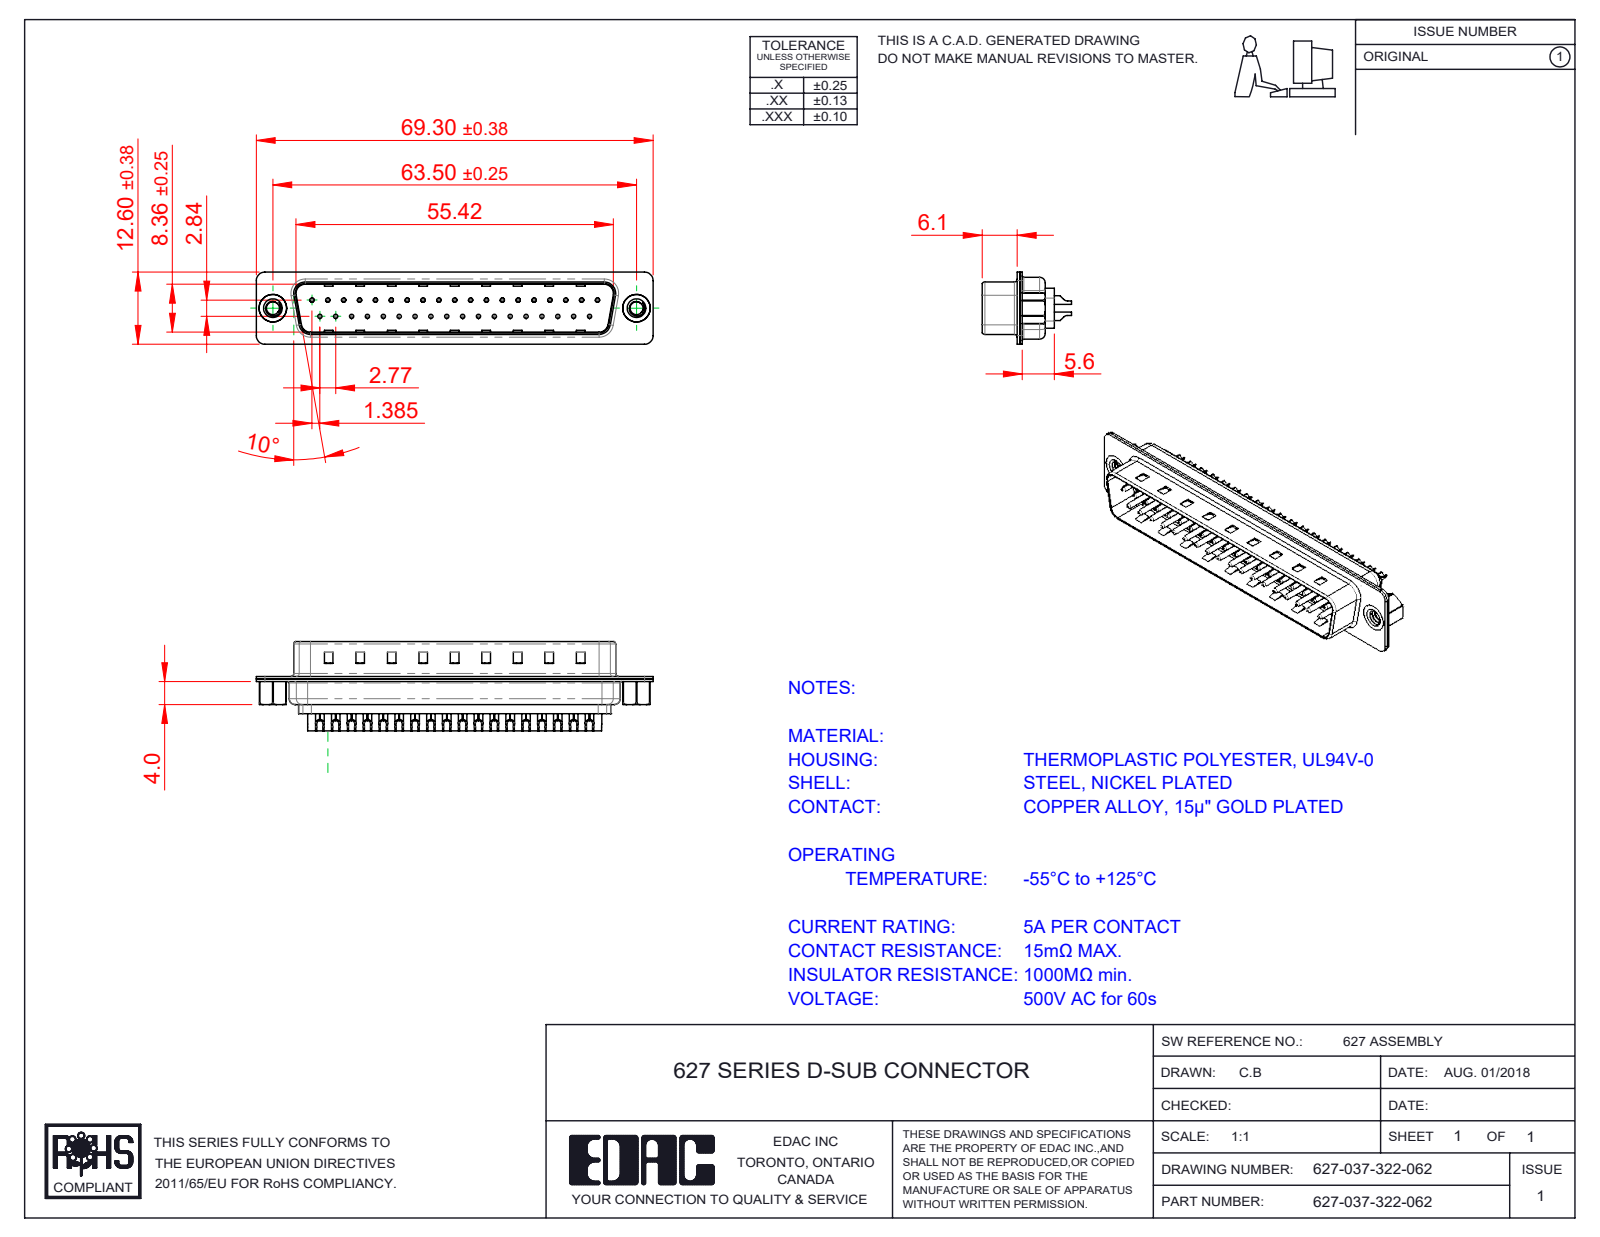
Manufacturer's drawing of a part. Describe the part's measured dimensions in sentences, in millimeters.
The part is named "627 Contact Row 1_22L; 627 Shell Rear_37 Contacts; 627-037-322-062; 627 Shell Front_37 Contacts (+3 more)". Its 3-D file was written by "SolidWorks 2020 (CONFIG_CONTROL_DESIGN)". It is 42 solids with 2776 faces: 721 planar, 1212 cylindrical and 843 other. Overall it measures 69.3 by 15.35 by 12.6 millimeters. Its volume is 3 709 cubic millimeters and its surface area 10 747 square millimeters. Round holes: 37 of diameter 0.35, 37 of diameter 1.1, 37 of diameter 1.6, 2 of diameter 2.26, 2 of diameter 4, 2 of diameter 4.8. Round bosses or shafts: 37 of diameter 2, 37 of diameter 1.5, 37 of diameter 0.75, 2 of diameter 5, 2 of diameter 4.9. Partial cylindrical surfaces (rounded edges, fillets, slot ends): 16 of radius 1.5, 12 of radius 2, 8 of radius 0.5, 8 of radius 1.6, 6 of radius 1, 4 of radius 0.25, 4 of radius 0.6, 4 of radius 0.65. The main face-to-face distances are 0.4, 0.82, 9.58, 0.45, 8.76, 1.5, 0.9, 1.4, 6.05, 0.42. The hole center spacings are 3.16, 2.77, 5.54, 8.31, 5.04, 10.1, 11.08, 12.78.
